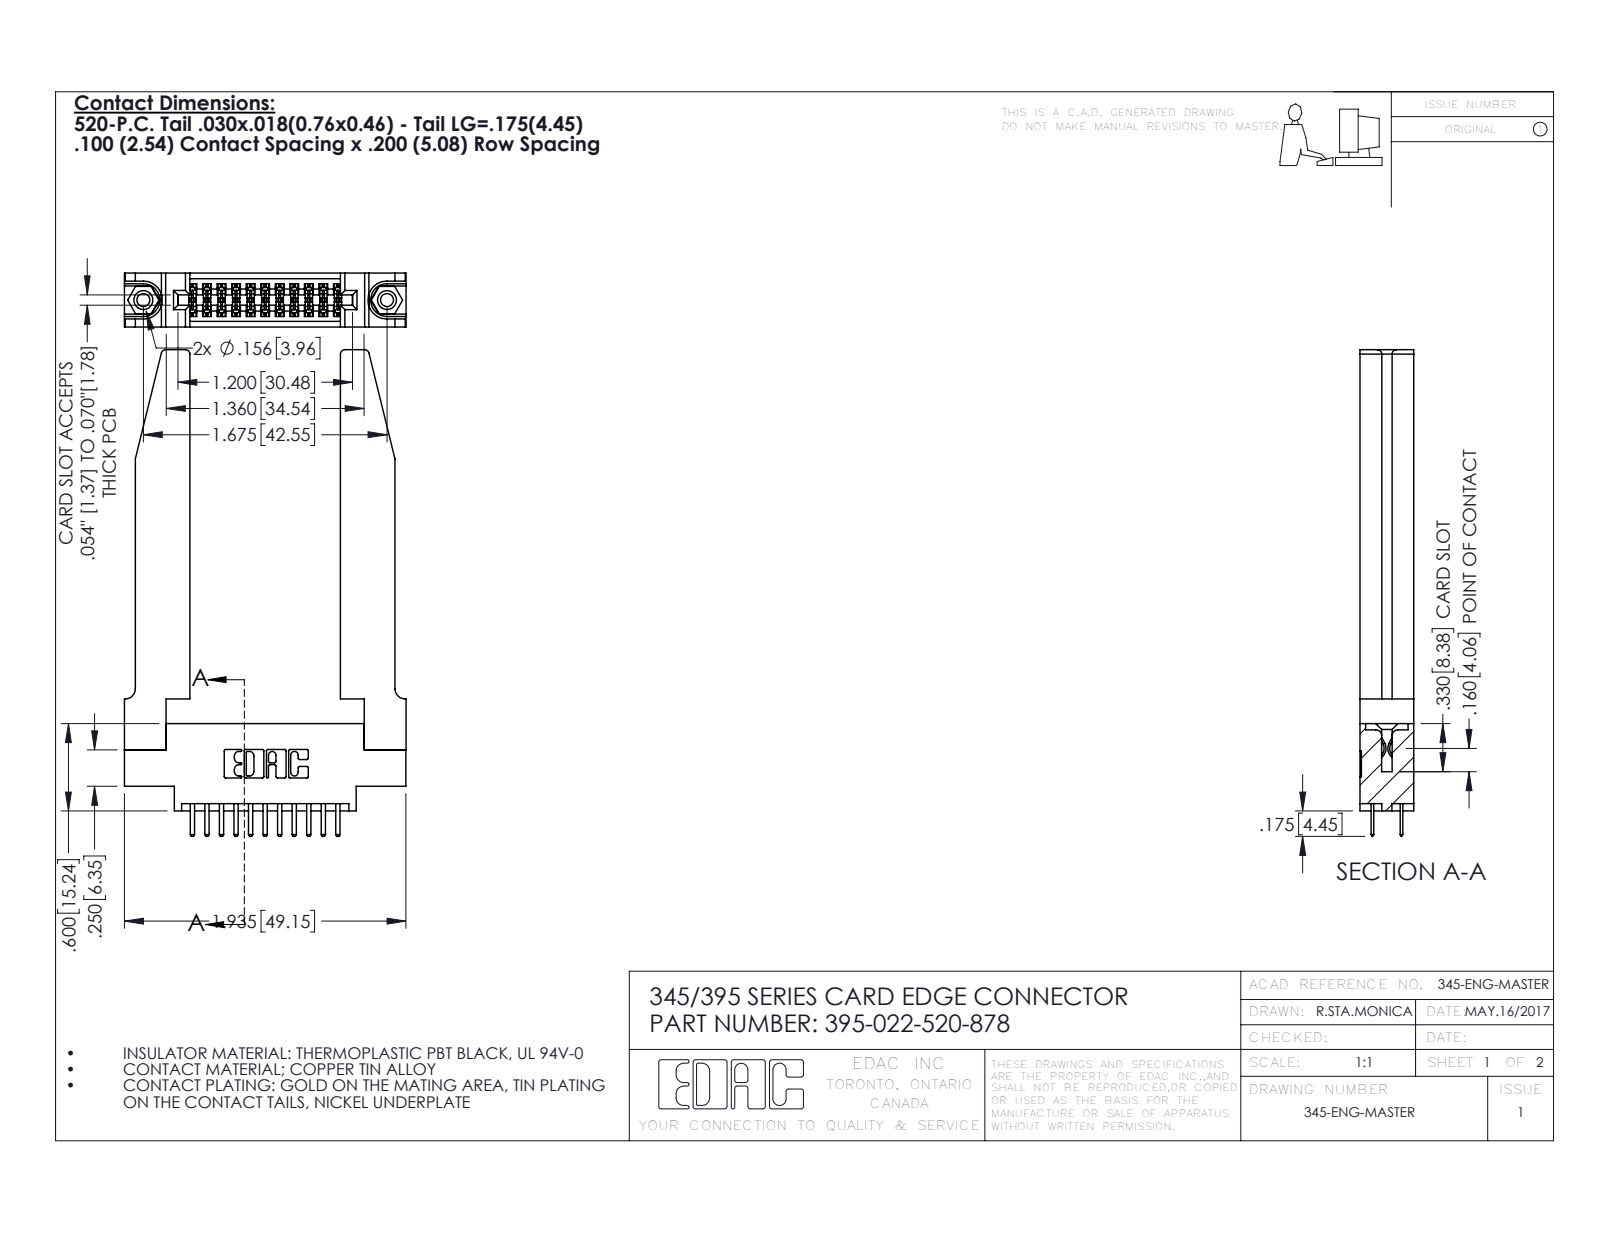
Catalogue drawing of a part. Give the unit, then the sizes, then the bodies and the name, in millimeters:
Units: millimetres
Overall size (bounding box): 85 × 49.2 × 9.4
Round holes (diameter × count): ⌀2.3 ×2, ⌀3.2 ×2, ⌀4 ×2, ⌀1.6 ×1
Round bosses / shafts (diameter × count): ⌀3.9 ×2
Partial cylindrical surfaces — rounded edges, fillets, slot ends (radius × count): R0.2 ×33, R0.3 ×26, R0.3 ×22, R0.8 ×8, R0.2 ×6, R0.8 ×6, R0.7 ×3, R0.4 ×2
Main face-to-face distances: 9.4, 1.8, 7.6, 3.8, 5.6, 2, 3.8, 5.1, 26.3, 3.1
Hole centre spacings: 6.9, 36.7, 42.5
Volume: 12 100 mm³ · Surface area: 12 810 mm²
Bodies: 27 solids, 1552 faces (996 planar, 504 cylindrical, 52 other)
Part name (STEP PRODUCT): 345 Part_0.170 Offset - 0.156 Dia-TH; 345-292-001_345-293-120; 345-250-001_345-250-001-102; 345-220-078_345-220-078 (+1 more)
STEP written by: SolidWorks 2016 (CONFIG_CONTROL_DESIGN)
